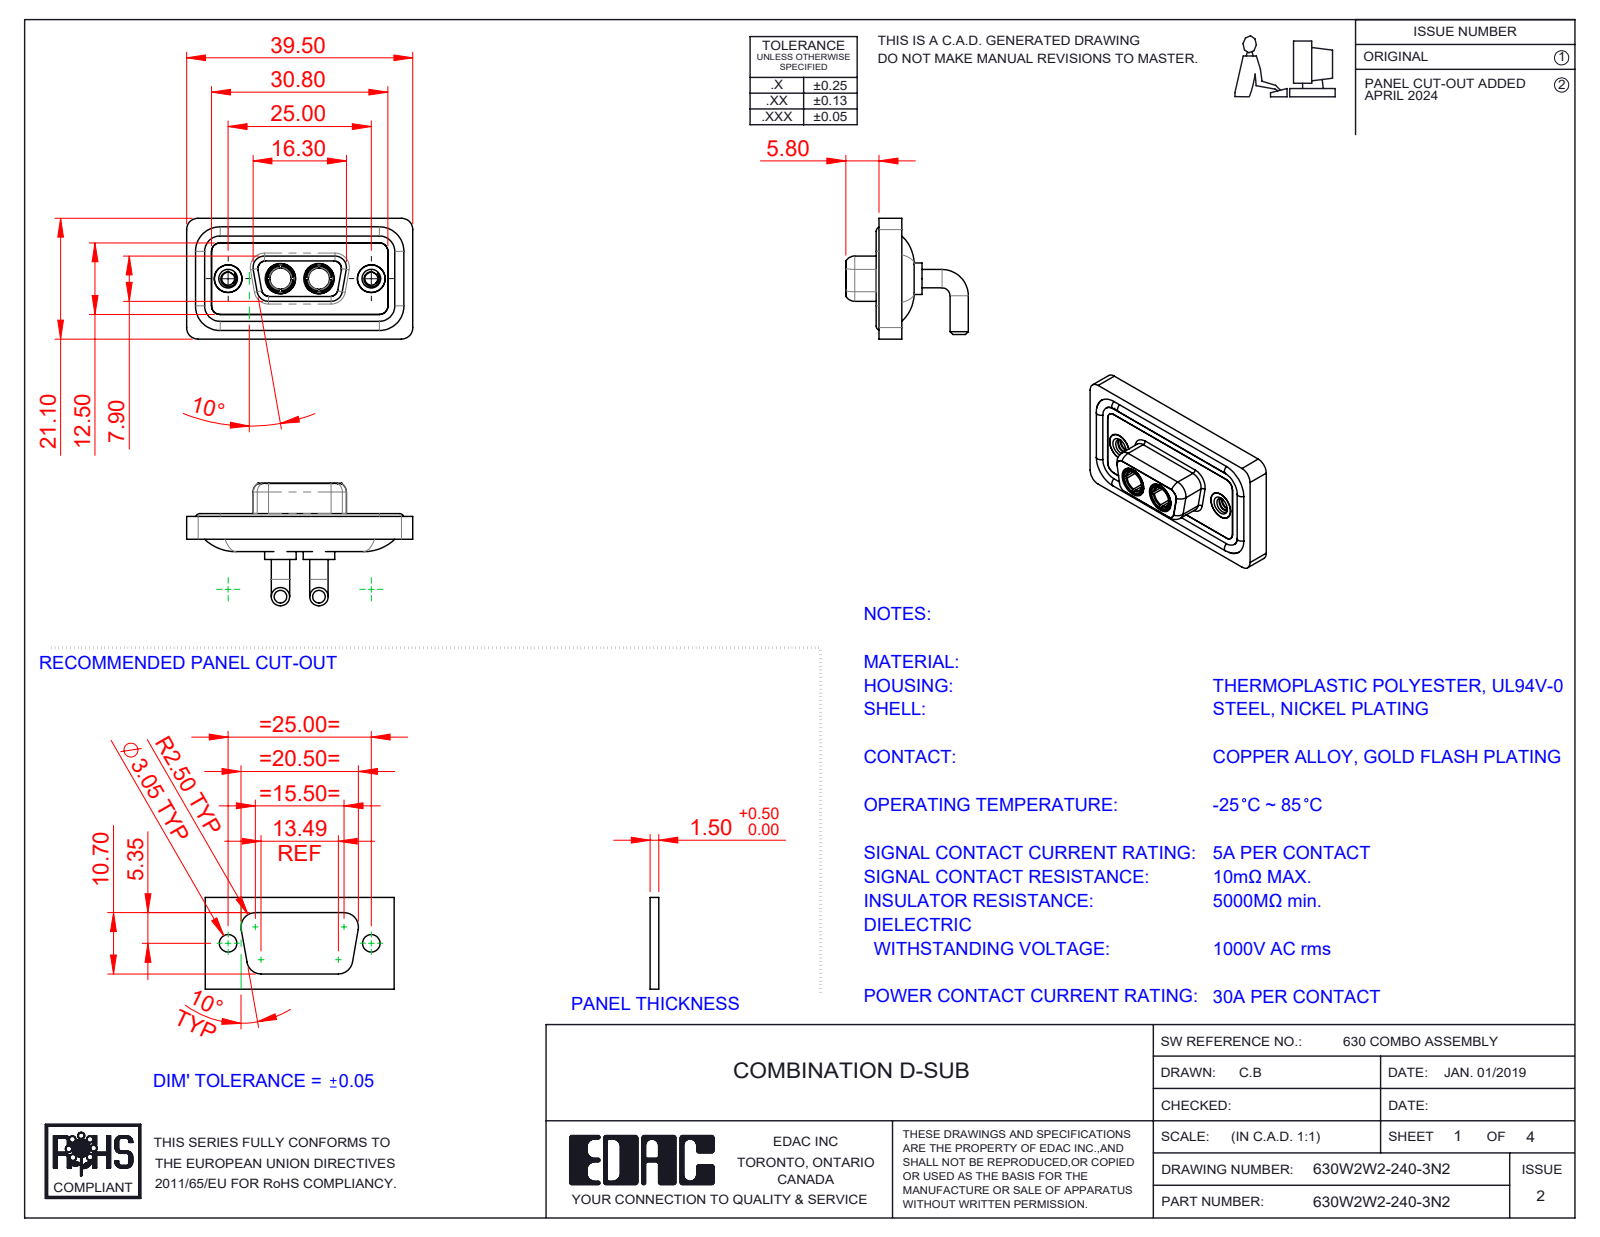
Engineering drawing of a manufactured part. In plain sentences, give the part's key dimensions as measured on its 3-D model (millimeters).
The part is named "630W2W2-140-3N2; 630Combo Housing_2W2; Power Socket_30A RA; 630Combo Shell Rear_09 Contacts (+3 more)". Its 3-D file was written by "SolidWorks 2023 (CONFIG_CONTROL_DESIGN)". It is 11 solids with 542 faces: 163 planar, 238 cylindrical and 141 other. Overall it measures 39.5 by 21.4 by 21.1 millimeters. Its volume is 4 872 cubic millimeters and its surface area 7 822 square millimeters. Round holes: 4 of diameter 4.85, 2 of diameter 2.26, 2 of diameter 3.7, 2 of diameter 4, 2 of diameter 4.05, 2 of diameter 5, 2 of diameter 5.3. Round bosses or shafts: 4 of diameter 3.2, 4 of diameter 1.6, 2 of diameter 5.5, 2 of diameter 5.2, 2 of diameter 4.96, 2 of diameter 4.95, 2 of diameter 4.8, 2 of diameter 4.75. Partial cylindrical surfaces (rounded edges, fillets, slot ends): 18 of radius 1.5, 18 of radius 2, 8 of radius 1.35, 8 of radius 1.6, 4 of radius 0.25, 4 of radius 0.5, 4 of radius 0.6, 4 of radius 0.65. The main face-to-face distances are 0.4, 1.8, 1.1, 2.9, 2.5, 1.6, 3.1, 1.5, 2.1, 0.5. The hole center spacings are 9.14, 15.86, 6.72, 25.
